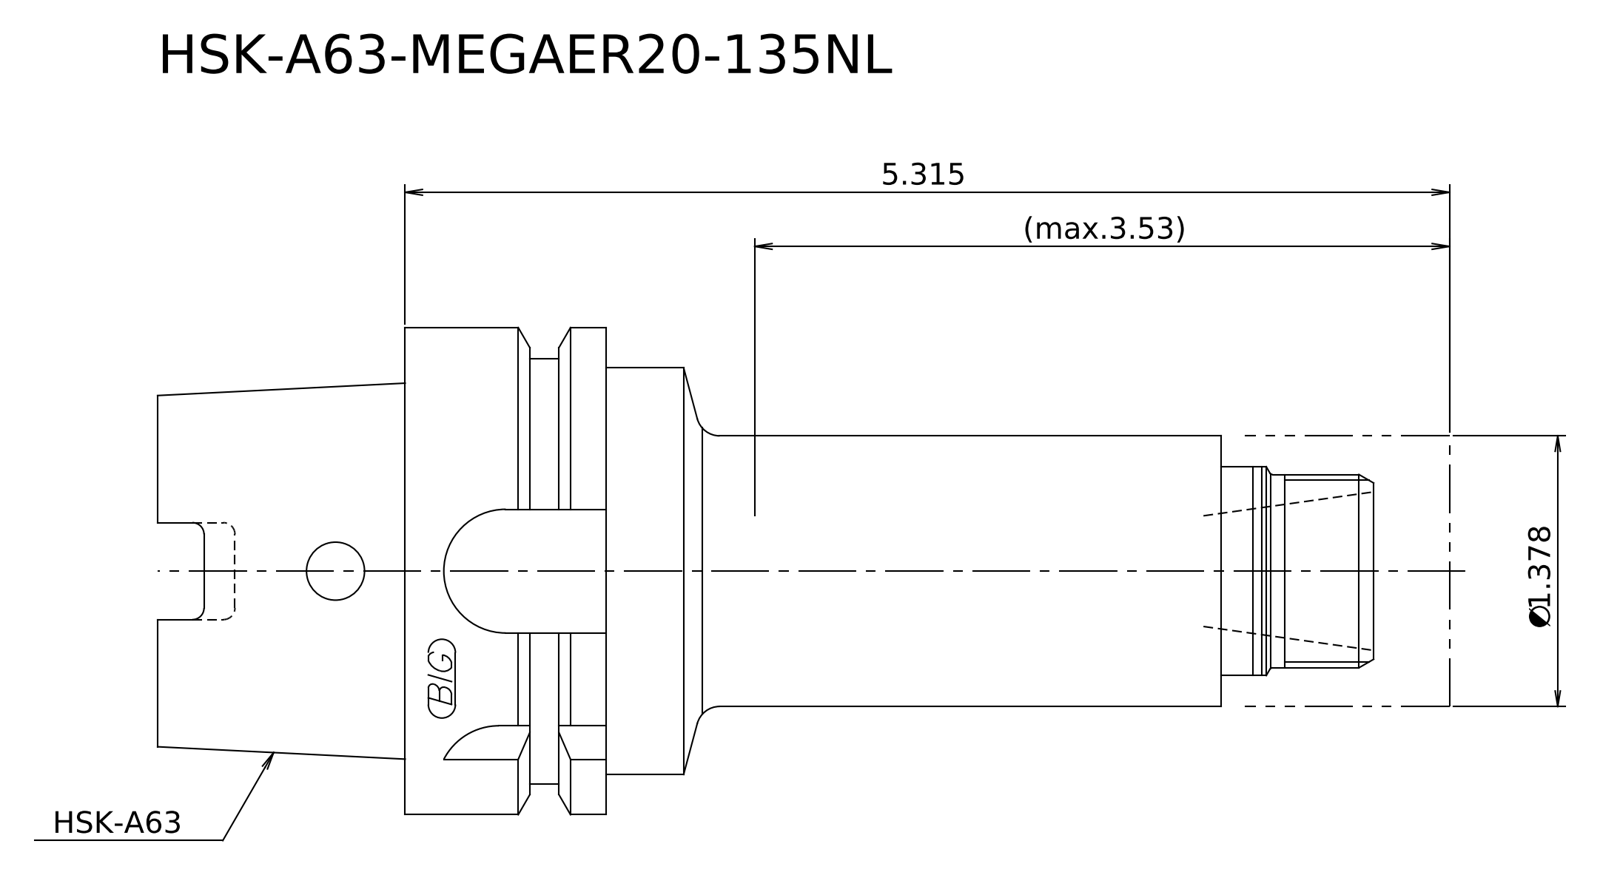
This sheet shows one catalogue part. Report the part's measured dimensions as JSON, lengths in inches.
{"step_written_by": "Kubotek KeyCreator 2011 V10.0.2 (22737) (automotive_design)", "units": "inches", "bodies": {"solids": 2, "faces": 23, "planar": 9, "cylindrical": 8, "other": 6}, "overall_size": [6.575, 2.48, 2.48], "volume_in3": 15.86, "surface_area_in2": 49.74, "round_bosses_or_shafts": [[2.48, 1], [2.165, 1], [2.071, 1], [1.378, 1], [1.063, 1], [0.984, 1]], "face_to_face_distances": [1.26, 4.272, 5.531, 1.043, 5.315, 6.575, 4.291, 3.248, 1.024, 2.283]}
